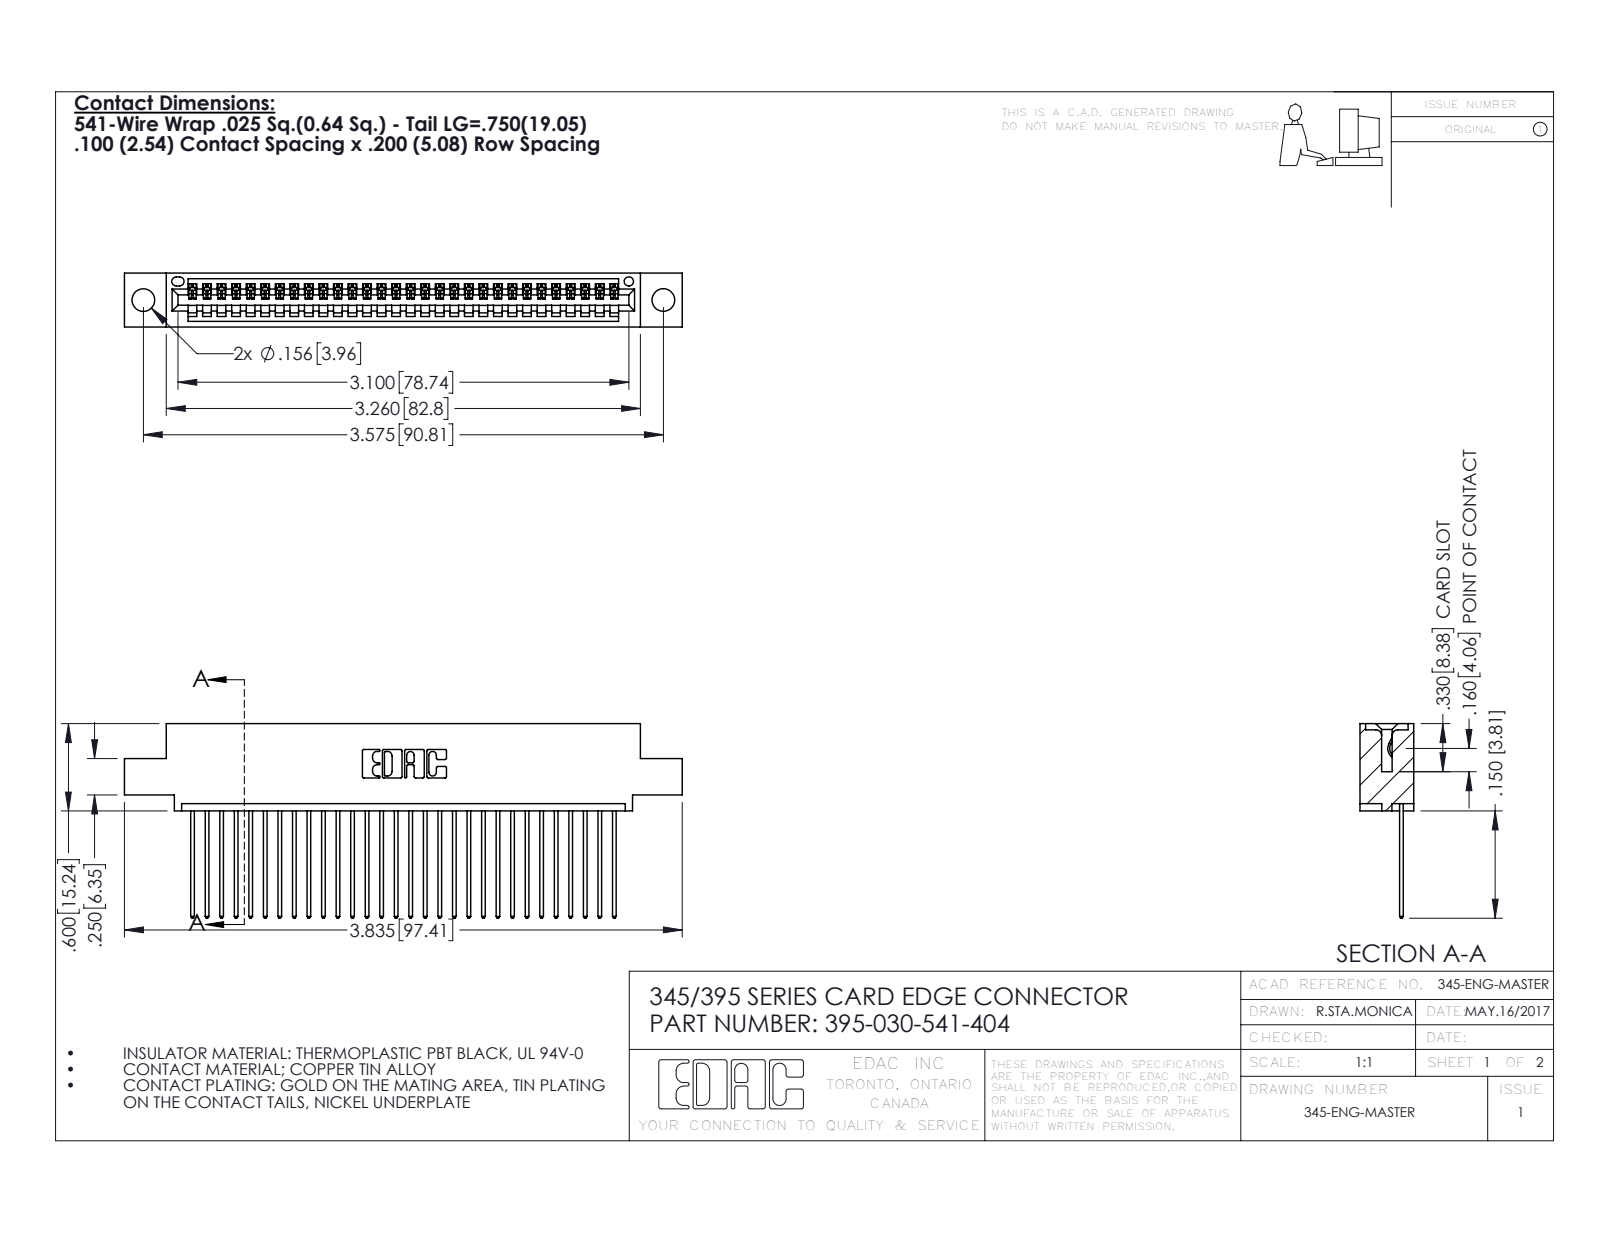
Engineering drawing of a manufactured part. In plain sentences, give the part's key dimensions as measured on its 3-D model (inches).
The part is named "395-030-541-404; 345-292-001_345-293-141; 345 Part_0.110 Offset - 0.156 Dia-TH". Its 3-D file was written by "SolidWorks 2016 (CONFIG_CONTROL_DESIGN)". It is 31 solids with 1870 faces: 1284 planar, 586 cylindrical and 0 other. Overall it measures 3.835 by 1.337 by 0.37 inches. Its volume is 0.555 cubic inches and its surface area 19.21 square inches. Round holes: 2 of diameter 0.156, 1 of diameter 0.064. Partial cylindrical surfaces (rounded edges, fillets, slot ends): 60 of radius 0.006, 60 of radius 0.01, 22 of radius 0.01, 6 of radius 0.007, 6 of radius 0.031, 3 of radius 0.026, 2 of radius 0.031, 2 of radius 0.04. The main face-to-face distances are 0.072, 0.298, 0.098, 0.272, 0.025, 0.37, 0.2, 0.225, 0.149, 0.072. The hole center spacings are 0.27, 3.34, 3.575.
